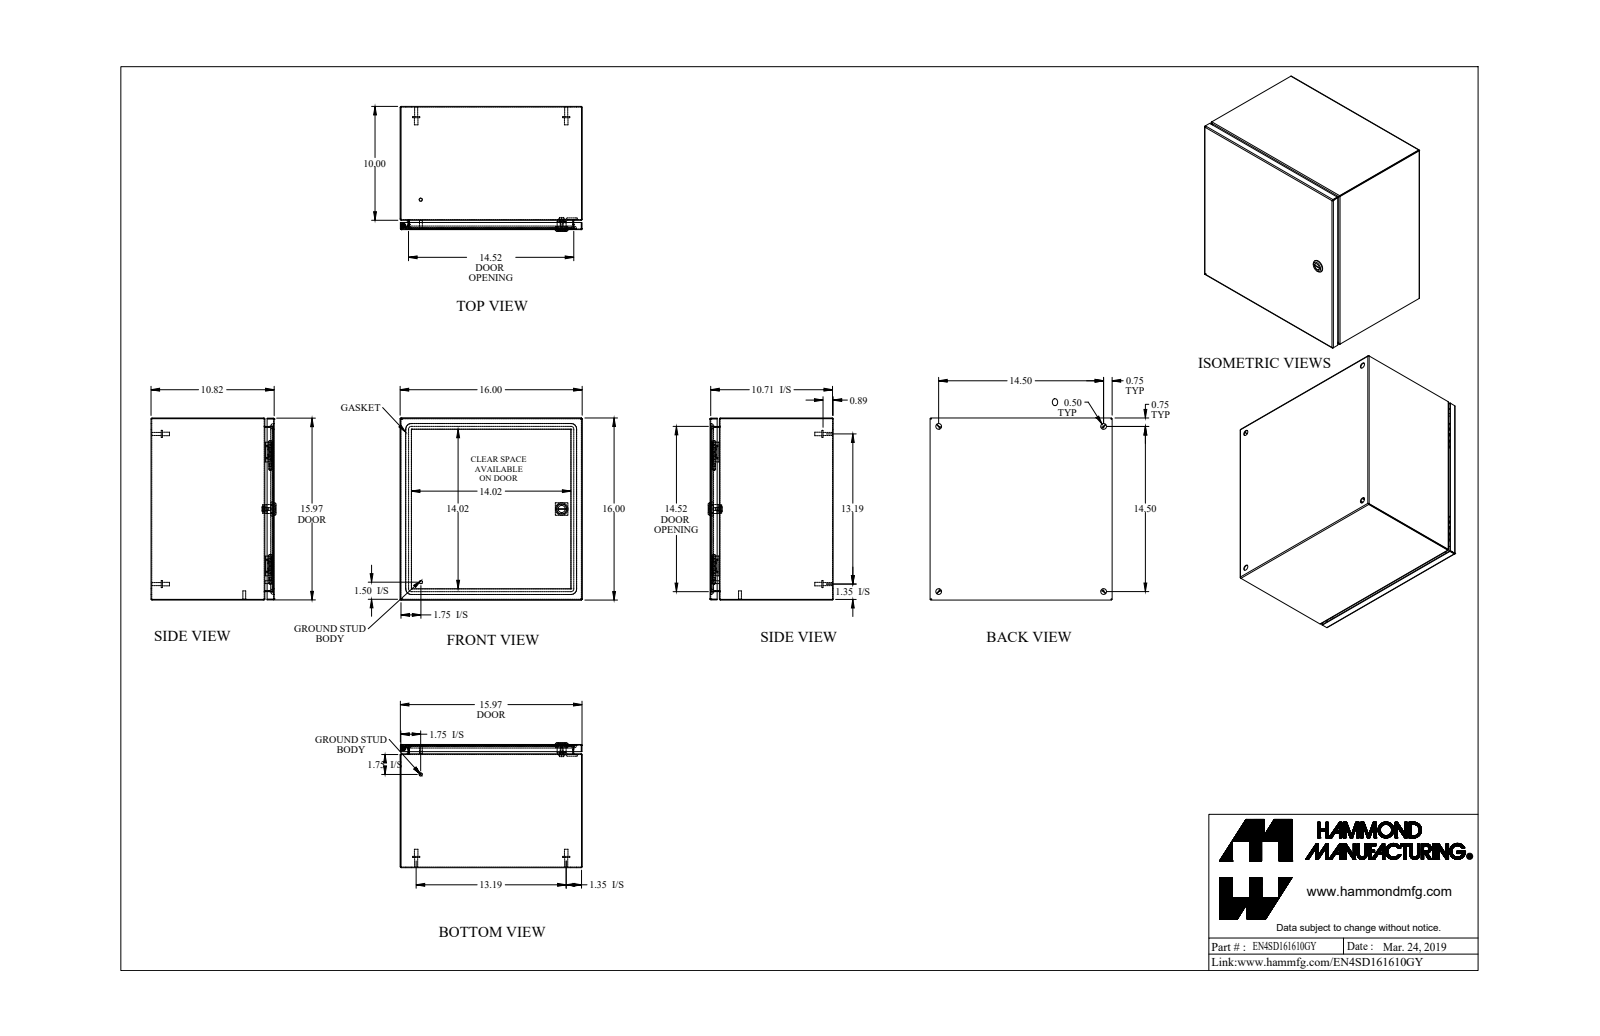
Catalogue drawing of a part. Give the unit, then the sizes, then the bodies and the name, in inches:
Units: inches
Overall size (bounding box): 16 × 16 × 10.982
Round holes (diameter × count): ⌀0.5 ×4, ⌀0.172 ×1, ⌀0.232 ×1, ⌀0.24 ×1, ⌀0.242 ×1, ⌀0.625 ×1, ⌀0.785 ×1
Round bosses / shafts (diameter × count): ⌀0.625 ×4, ⌀0.313 ×4, ⌀0.27 ×4, ⌀0.281 ×2, ⌀0.25 ×2, ⌀1.1 ×1, ⌀0.525 ×1, ⌀0.455 ×1
Partial cylindrical surfaces — rounded edges, fillets, slot ends (radius × count): R0.029 ×21, R0.086 ×21, R0.25 ×16, R19 ×8, R0.006 ×4, R0.062 ×4, R0.499 ×4, R0.125 ×2
Main face-to-face distances: 0.057, 15.943, 10.765, 15.886, 16, 10.708, 10.822, 0.822, 9.943, 0.749
Hole centre spacings: 14.5, 20.506, 7.326, 7.327, 15.271, 15.272
Volume: 79.14 in³ · Surface area: 2 695 in²
Bodies: 21 solids, 634 faces (285 planar, 213 cylindrical, 136 other)
Part name (STEP PRODUCT): EN4SD161610GY_Default
STEP written by: SolidWorks 2019 (CONFIG_CONTROL_DESIGN)
